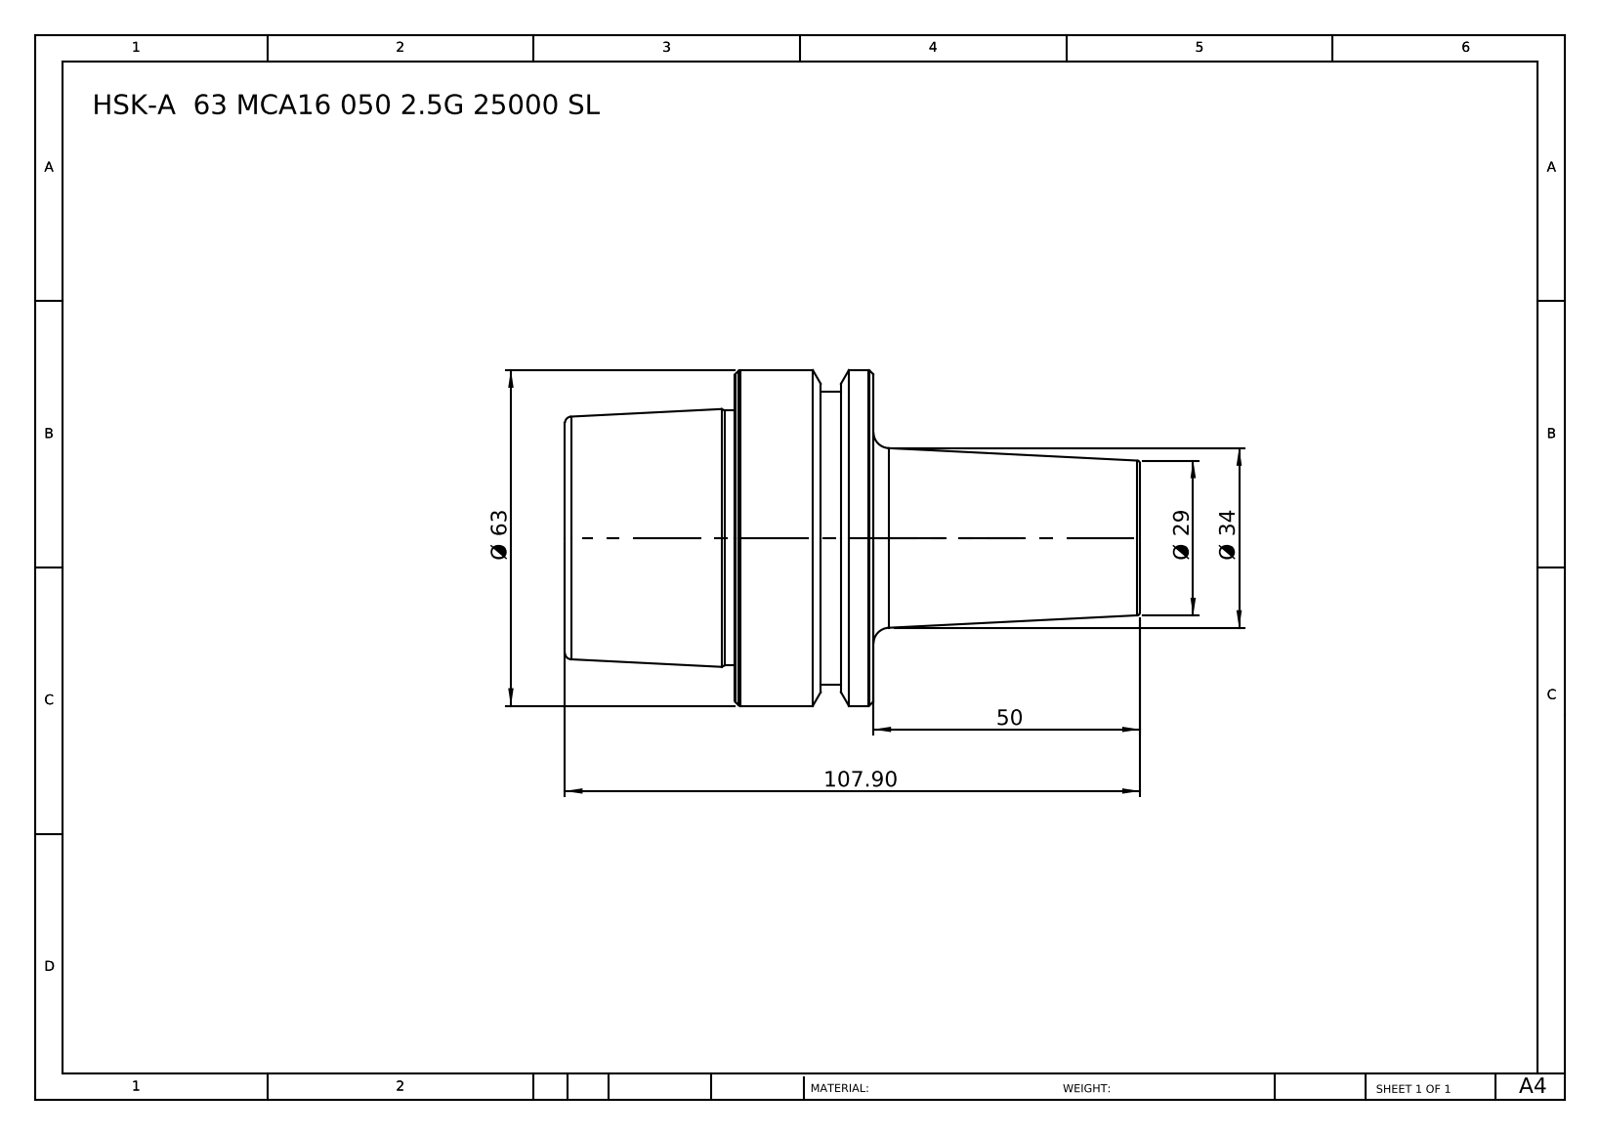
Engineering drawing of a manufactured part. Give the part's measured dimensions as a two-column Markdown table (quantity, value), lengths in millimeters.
| quantity | value |
| --- | --- |
| part name | HSK-A 63 MCA16 050 2.5G 25000 SL |
| STEP written by | SolidWorks 2014 (CONFIG_CONTROL_DESIGN) |
| units | millimeters |
| bodies | 1 solid, 46 faces (6 planar, 8 cylindrical, 32 other) |
| overall size | 107.9 × 63 × 63 |
| volume | 171 829 mm³ |
| surface area | 21 220 mm² |
| round bosses / shafts (diameter × count) | 63 × 1, 55 × 1, 47.78 × 1 |
| main face-to-face distances | 57.9, 26, 31.9, 50, 76, 107.9, 56.1, 6.1, 19.9, 51.8 |
